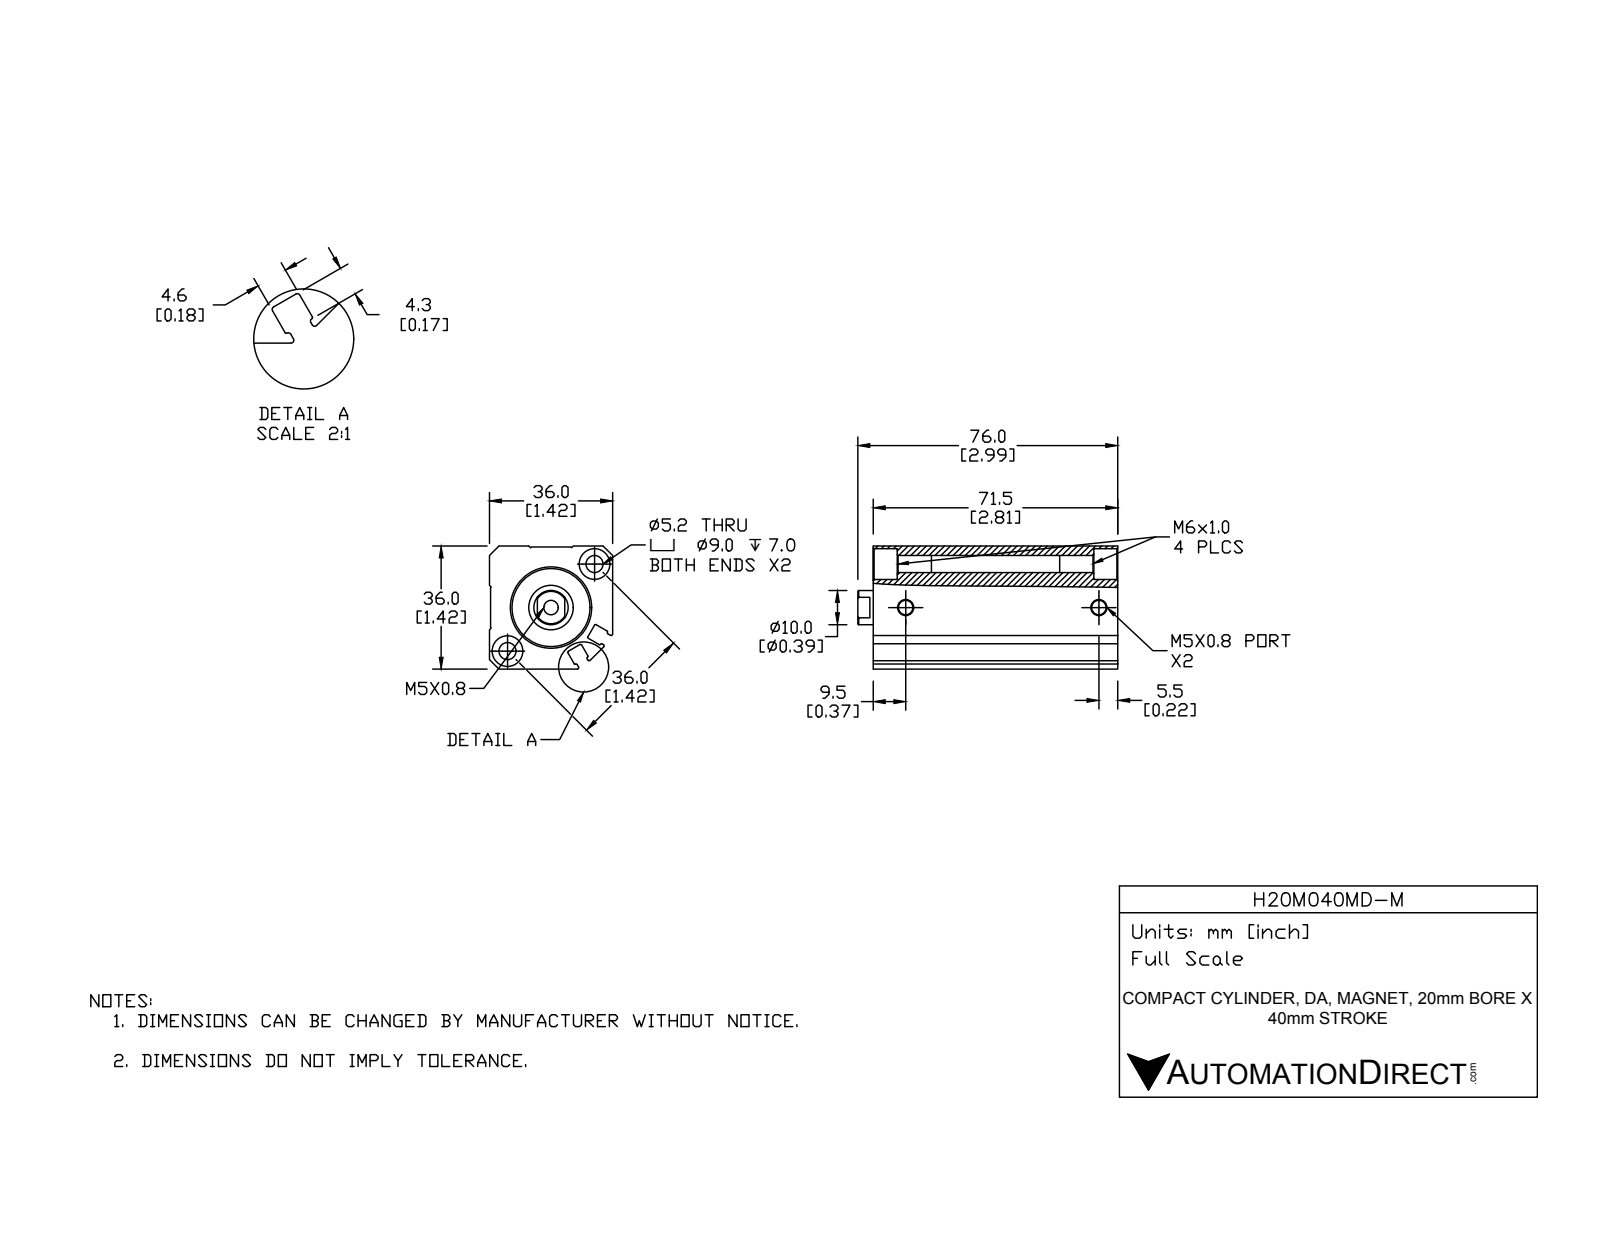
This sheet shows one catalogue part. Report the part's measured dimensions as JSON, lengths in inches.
{"part_name": "H20M040MD-M-BODY; H20M040MD-M-PISTON; H20M040MD-M", "step_written_by": "SolidWorks 2015 (CONFIG_CONTROL_DESIGN)", "units": "inches", "bodies": {"solids": 2, "faces": 141, "planar": 53, "cylindrical": 55, "other": 33}, "overall_size": [2.992, 1.417, 1.417], "volume_in3": 4.267, "surface_area_in2": 38.33, "round_holes": [[0.165, 3], [0.197, 2], [0.354, 2], [0.394, 1], [0.512, 1], [0.787, 1], [0.898, 1]], "round_bosses_or_shafts": [[0.433, 1]], "partial_cylinders_radius": [[0.016, 12], [0.008, 4]], "face_to_face_distances": [1.417, 1.406, 0.157, 2.815, 2.657, 0.181, 0.102, 0.055, 2.76, 2.382], "hole_center_spacings": [0.709, 1.418, 2.224]}
